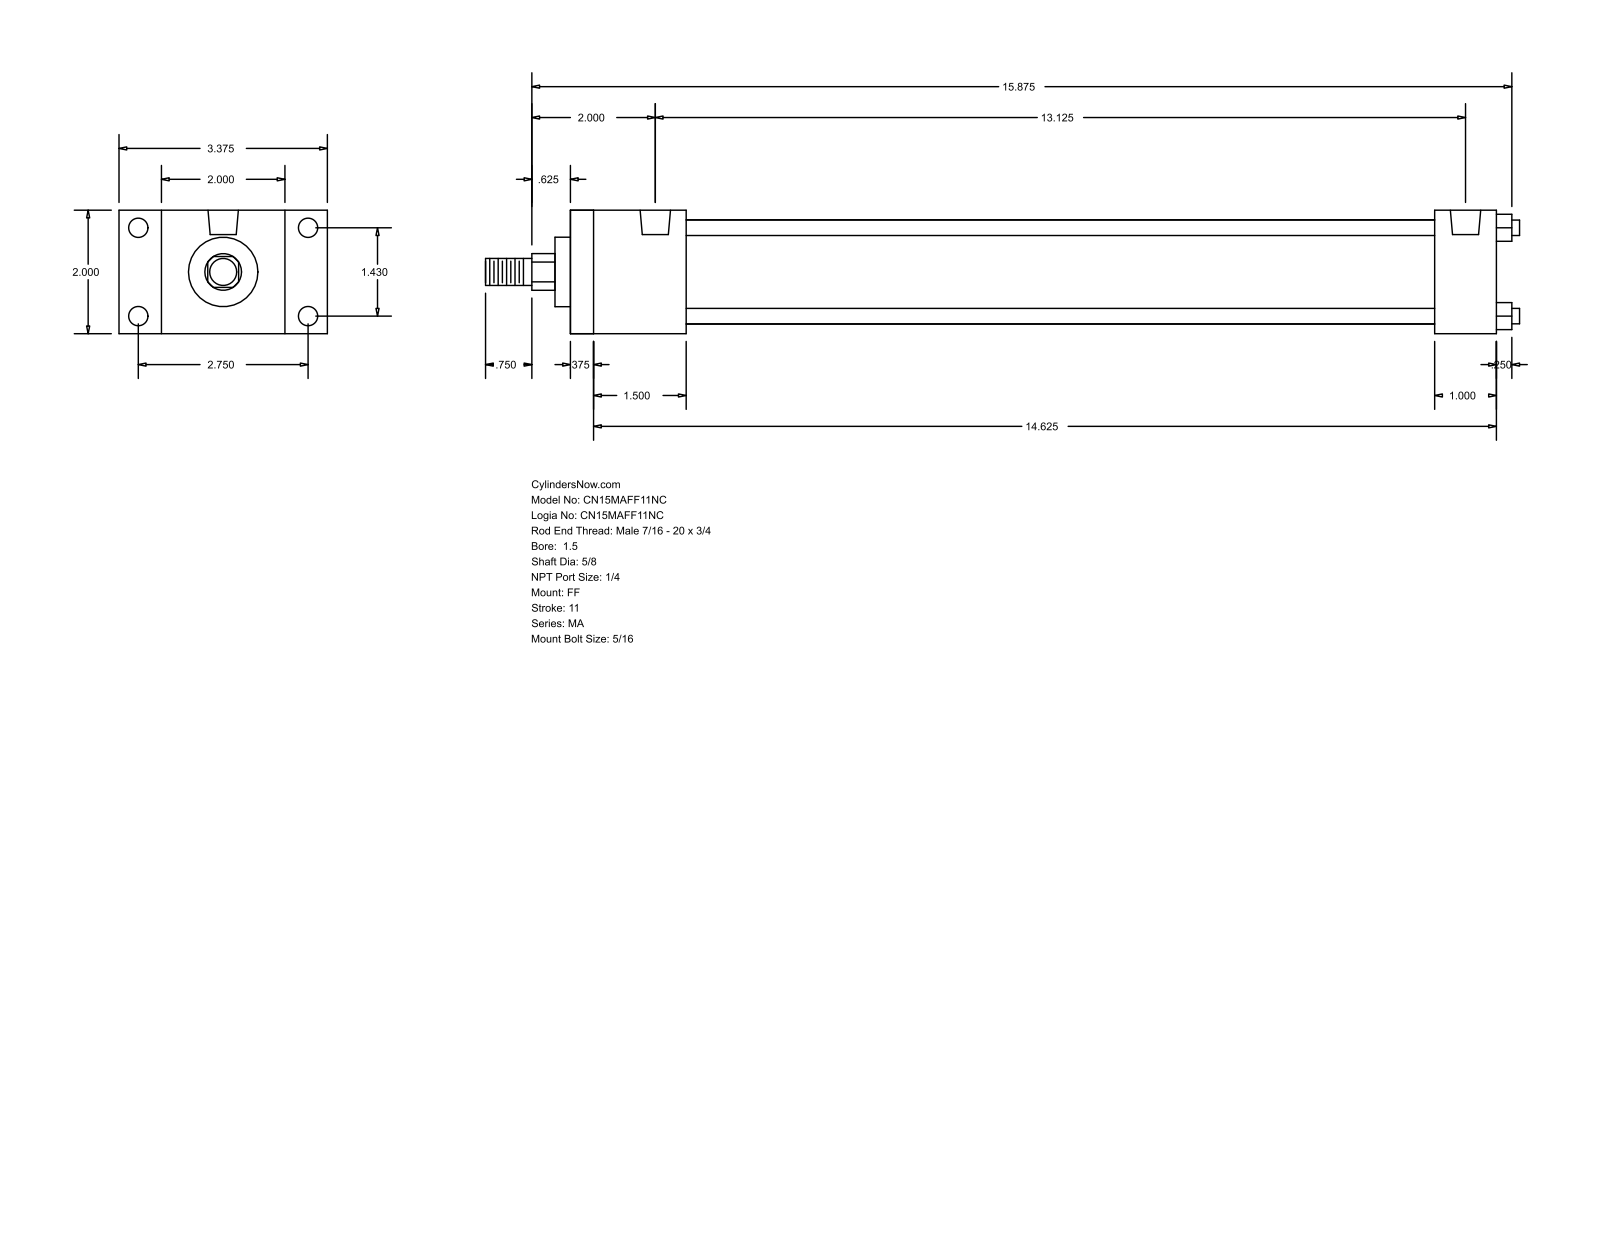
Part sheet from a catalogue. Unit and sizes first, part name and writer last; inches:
Units: inches
Overall size (bounding box): 16.75 × 3.375 × 2
Round holes (diameter × count): ⌀0.313 ×8, ⌀0.492 ×2
Round bosses / shafts (diameter × count): ⌀0.25 ×4, ⌀1.69 ×1, ⌀1.125 ×1, ⌀0.625 ×1, ⌀0.437 ×1
Partial cylindrical surfaces — rounded edges, fillets, slot ends (radius × count): R0.297 ×1
Main face-to-face distances: 2, 15, 0.375, 14.625, 1, 1.875, 14, 1.5, 13.625, 12.125
Hole centre spacings: 1.43, 2.75, 3.099, 13.125
Bodies: 0 solids, 92 faces (64 planar, 28 cylindrical, 0 other)
Part name (STEP PRODUCT): MA_FF__0150_0.625
STEP written by: GSSL Pune (CONFIG_CONTROL_DESIGN)
